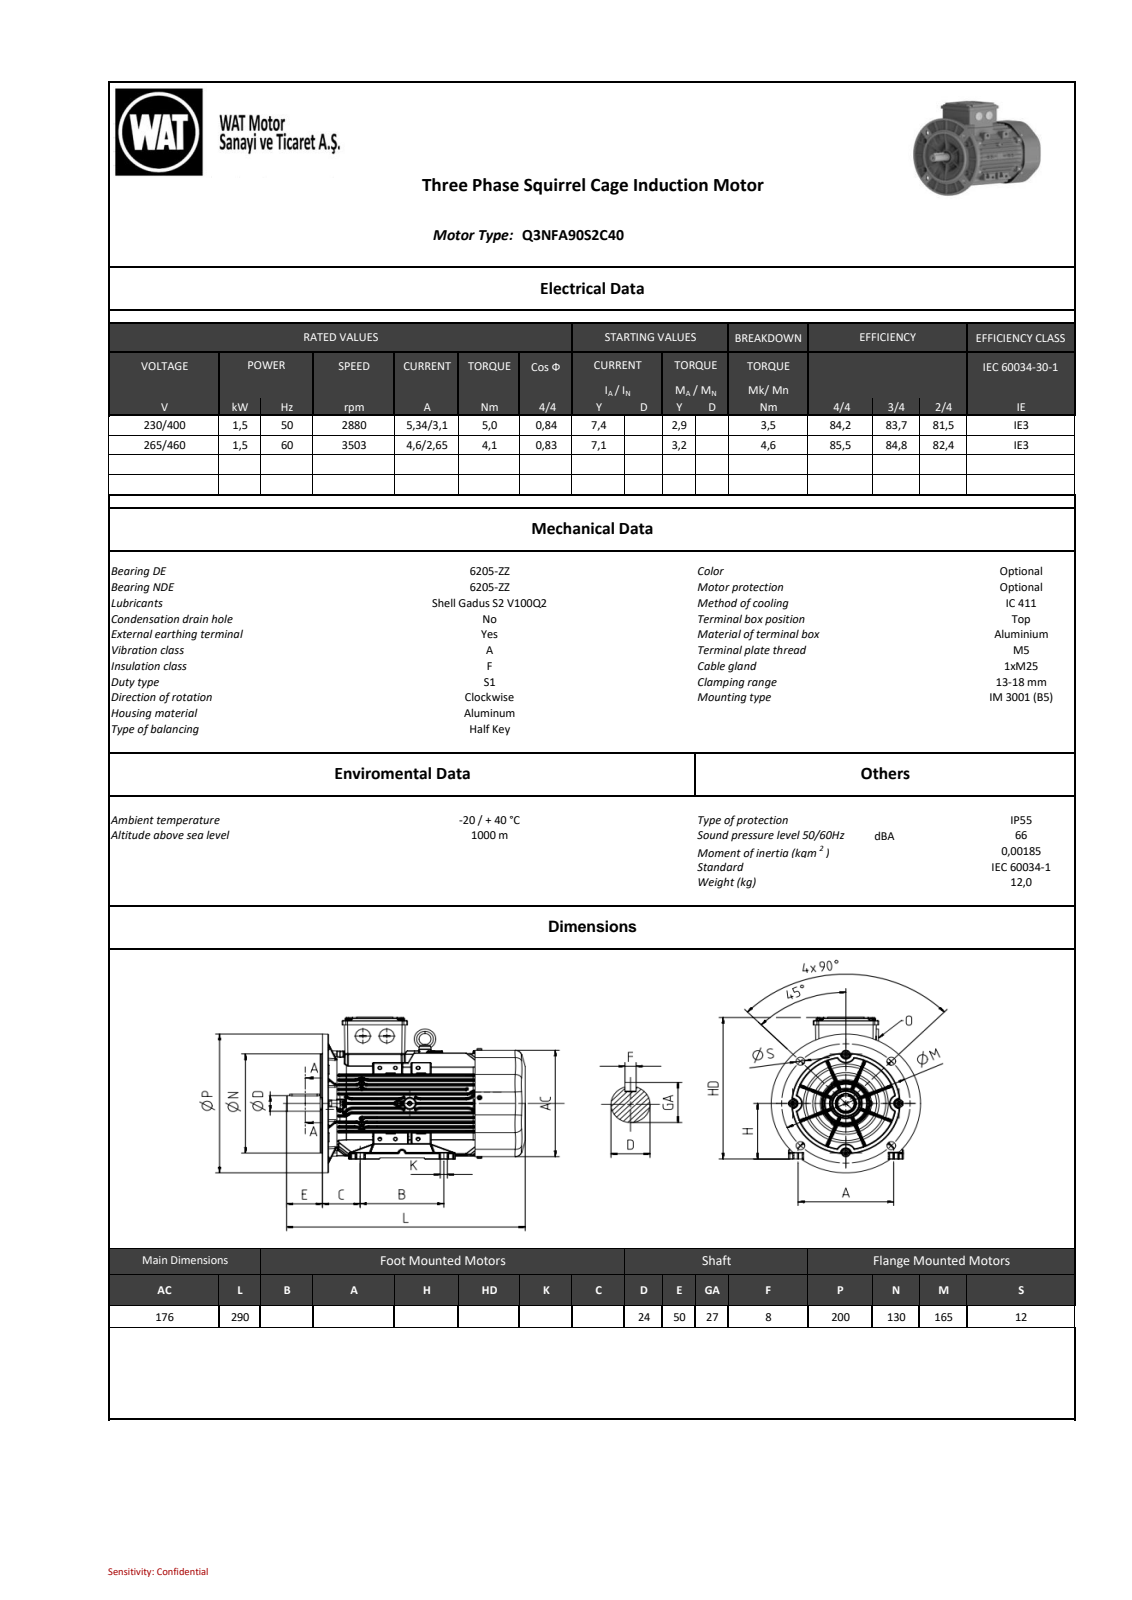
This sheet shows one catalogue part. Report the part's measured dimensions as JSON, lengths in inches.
{"part_name": "C901491873F3whh2", "step_written_by": "SIEMENS PLM Software NX 11.0 (AUTOMOTIVE_DESIGN)", "units": "inches", "bodies": {"solids": 0, "faces": 16697, "planar": 3890, "cylindrical": 5202, "other": 7605}, "overall_size": [11.417, 8.641, 7.833], "round_holes": [[0.165, 10], [0.201, 10], [0.354, 6], [0.118, 4], [0.472, 4], [0.276, 2], [0.157, 1], [0.315, 1], [0.48, 1], [1.1, 1], [1.142, 1], [1.181, 1]], "round_bosses_or_shafts": [[0.197, 16], [0.362, 10], [0.335, 10], [0.315, 8], [0.157, 8], [0.37, 6], [0.984, 3], [1.378, 2]], "partial_cylinders_radius": [[0.02, 1438], [0.039, 732], [0.031, 559], [0.008, 248], [0.059, 135], [0.012, 108], [0.157, 82], [0.079, 77]], "face_to_face_distances": [0.217, 0.031, 0.079, 0.236, 2.205, 2.756, 1.102, 5.709, 0.217, 0.229], "hole_center_spacings": [0.787, 1.575, 3.189, 0.557, 0.557, 1.113, 3.659, 5.224]}
